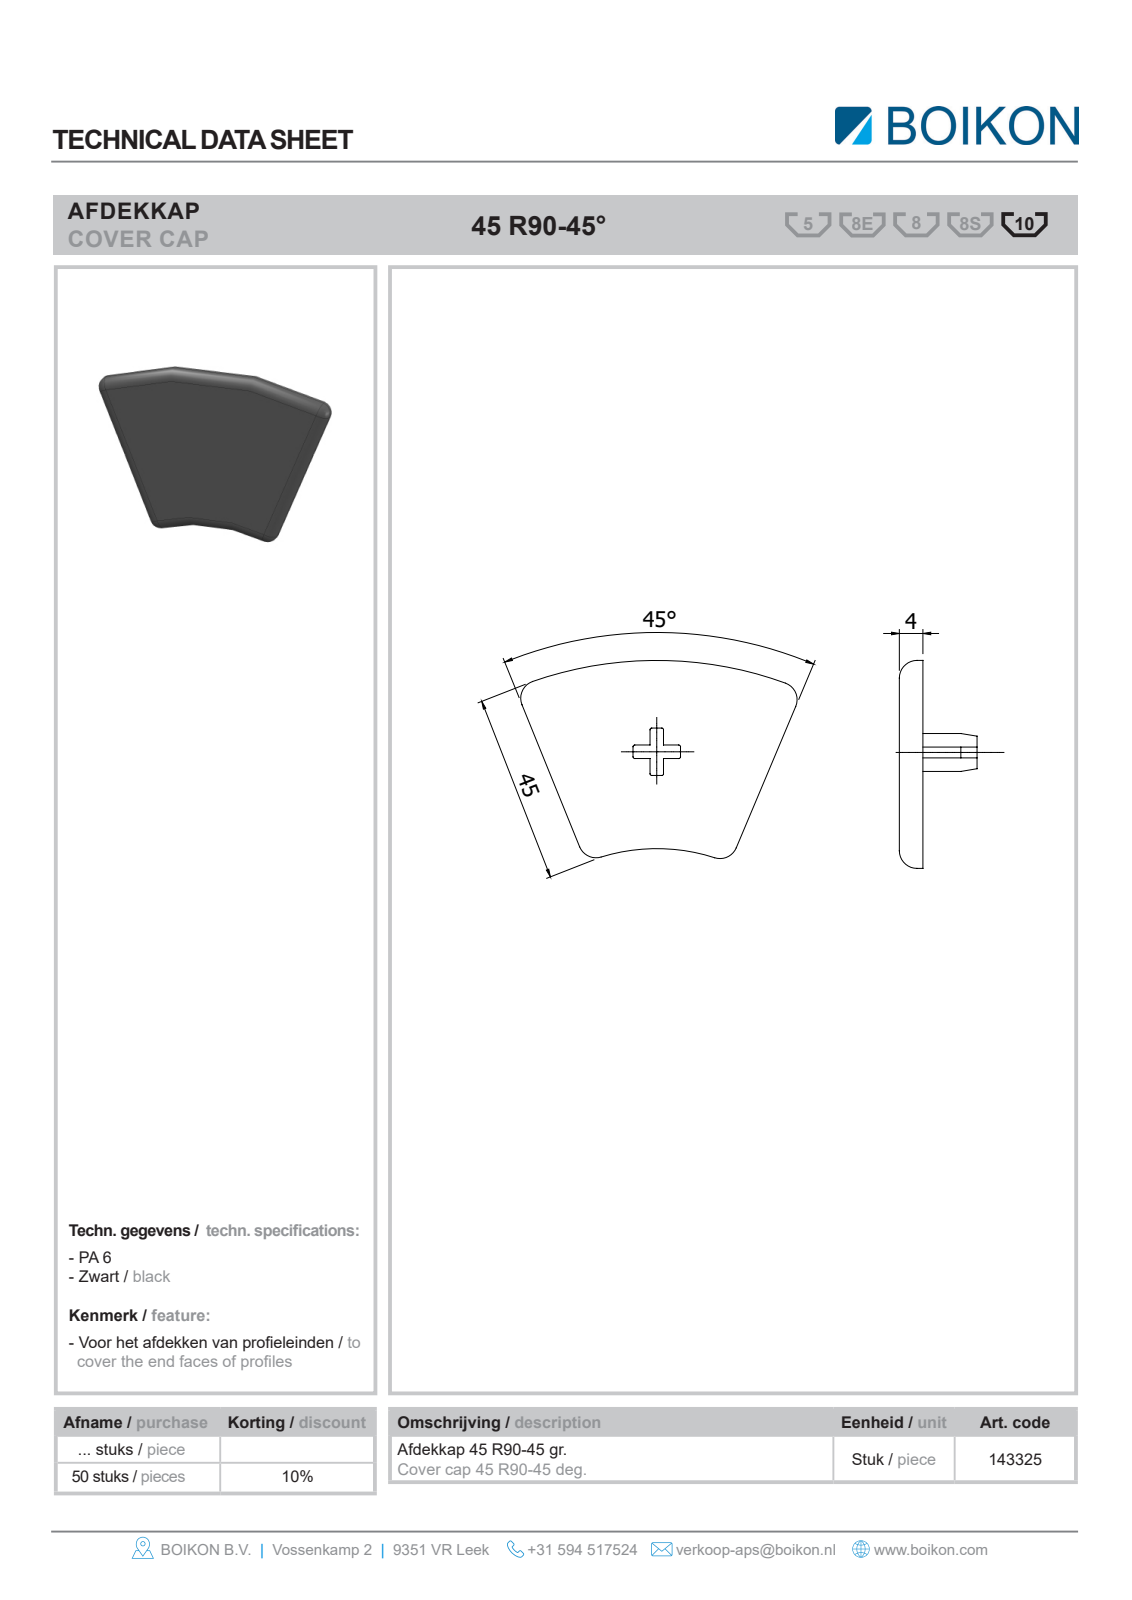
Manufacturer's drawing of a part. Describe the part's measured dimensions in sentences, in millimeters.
The part is named "Root; 143325Afdekkap 45-45GRBOIKON". Its 3-D file was written by "HiCAD 2013 1802.4 Build 509 (AUTOMOTIVE_DESIGN)". It is 1 solid with 18 faces: 4 planar, 8 cylindrical and 6 other. Overall it measures 62.36 by 56.95 by 4 millimeters. Its volume is 9 152 cubic millimeters and its surface area 5 270 square millimeters. Partial cylindrical surfaces (rounded edges, fillets, slot ends): 6 of radius 3, 1 of radius 45, 1 of radius 90. The main face-to-face distances are 4.
